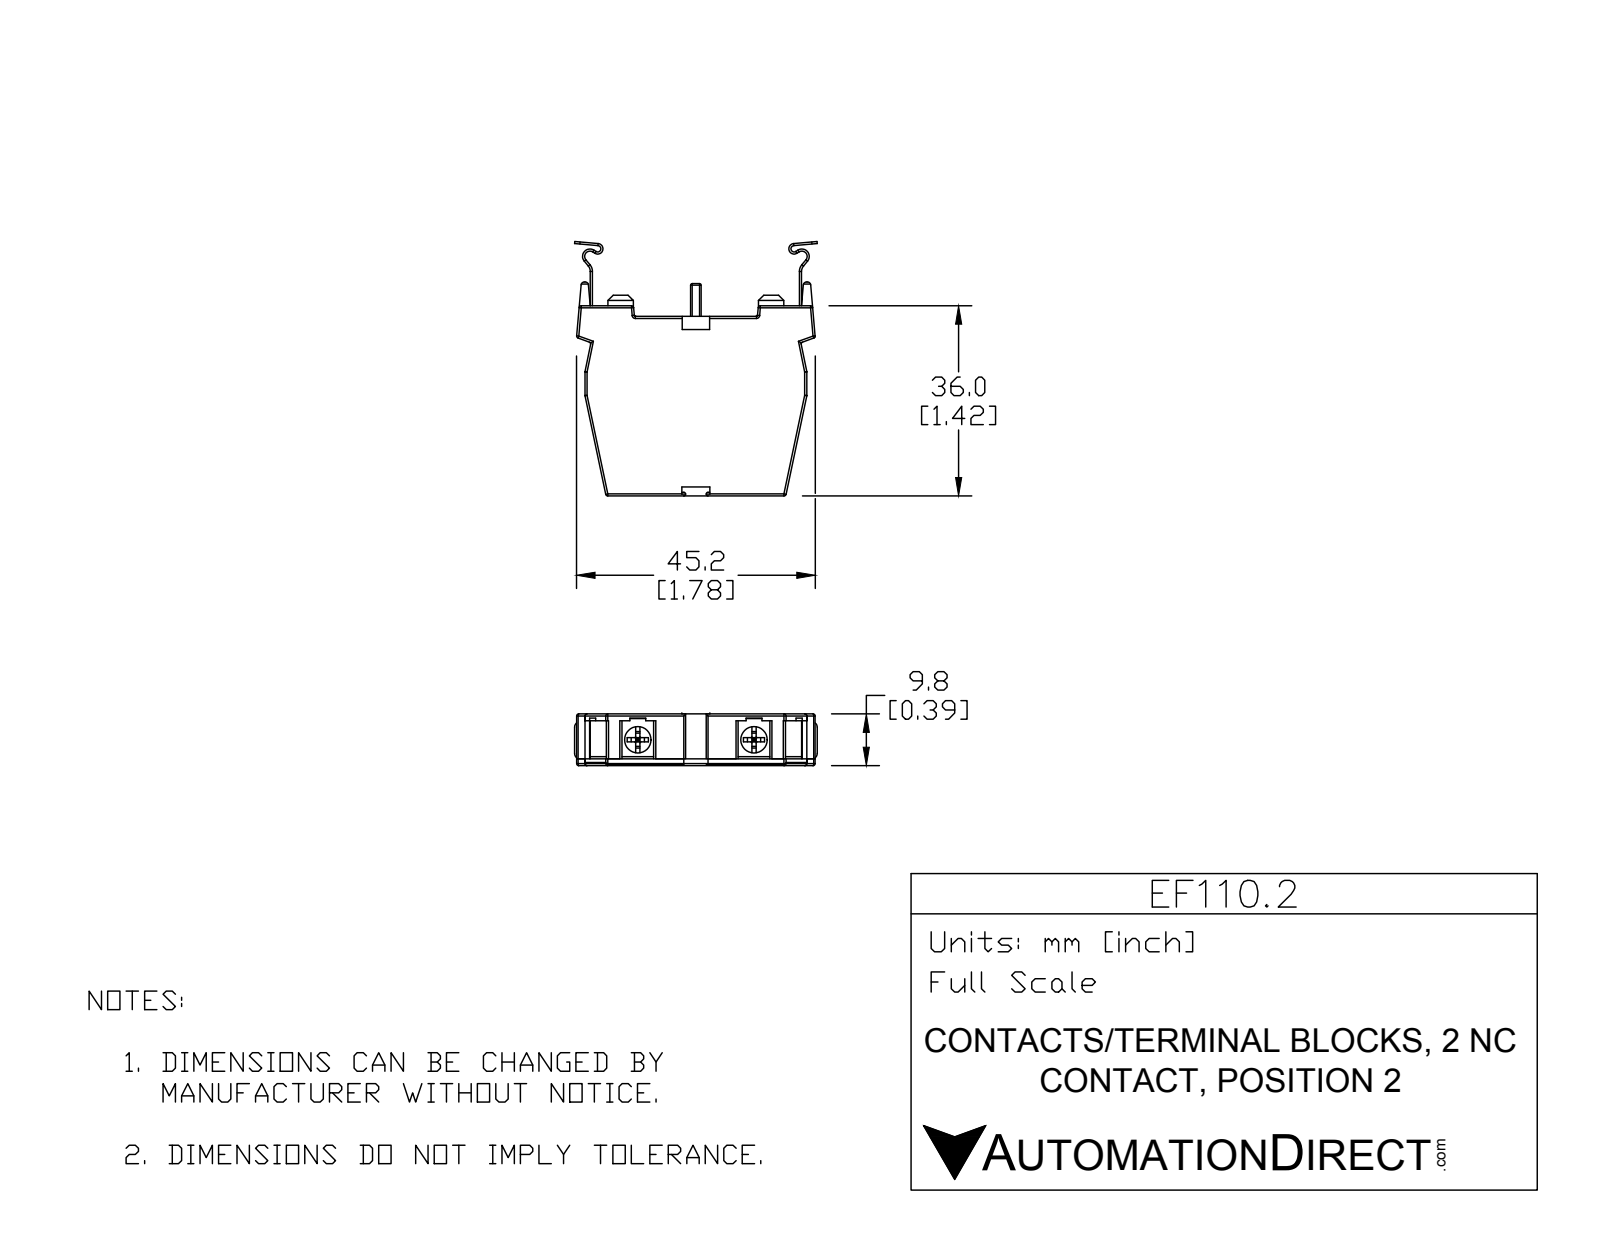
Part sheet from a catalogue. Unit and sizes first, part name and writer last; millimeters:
Units: millimetres
Overall size (bounding box): 48.16 × 46.28 × 9.8
Round holes (diameter × count): ⌀5 ×4
Round bosses / shafts (diameter × count): ⌀4 ×4, ⌀4.75 ×2
Partial cylindrical surfaces — rounded edges, fillets, slot ends (radius × count): R0.25 ×44, R0.5 ×8, R1 ×6, R0.6 ×4, R0.6 ×2, R1 ×2, R1.4 ×2, R1.6 ×2
Main face-to-face distances: 9.8, 1.4, 8.4, 34, 7, 2, 0.4, 3.18, 37.18, 36
Hole centre spacings: 21.81
Volume: 12 135 mm³ · Surface area: 6 604 mm²
Bodies: 7 solids, 299 faces (173 planar, 104 cylindrical, 22 other)
Part name (STEP PRODUCT): EF110.2
STEP written by: SolidWorks 2015 (AUTOMOTIVE_DESIGN)
